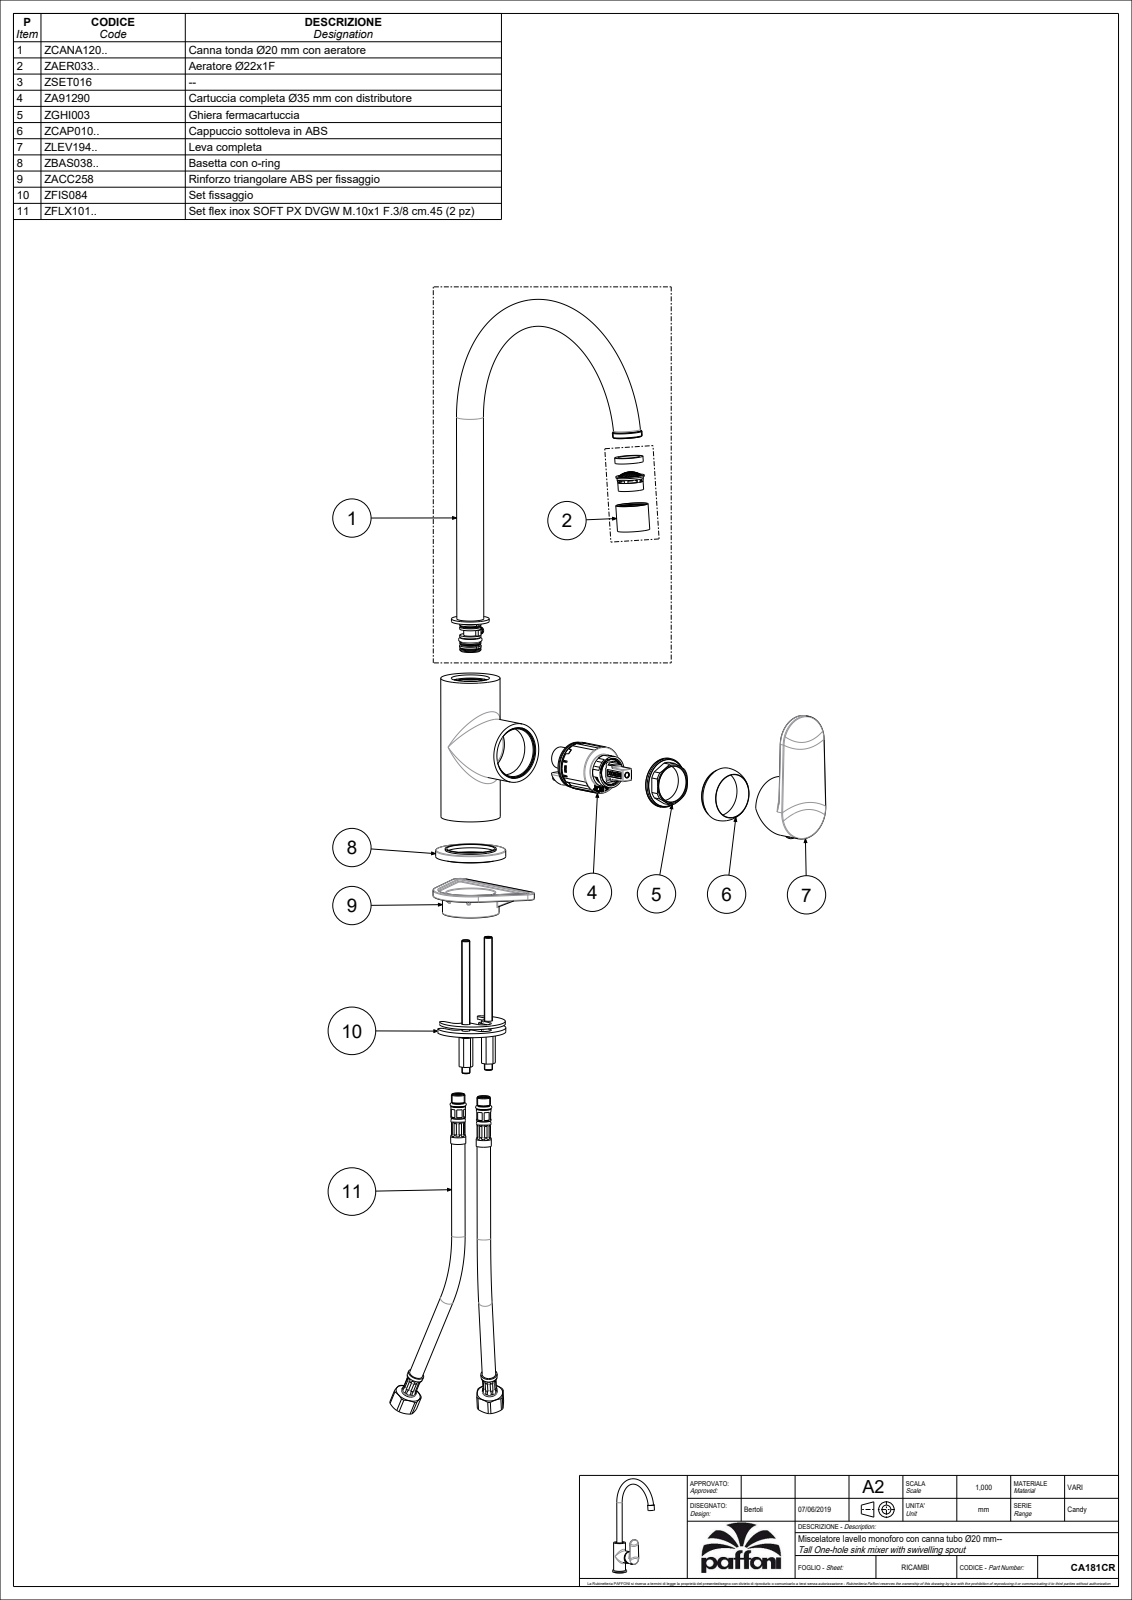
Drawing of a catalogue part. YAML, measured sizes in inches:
part_name: "CA181CR"
step_written_by: "CREO PARAMETRIC BY PTC INC, 2020044 (CONFIG_CONTROL_DESIGN)"
units: inches
bodies: {solids: 2, faces: 346, planar: 93, cylindrical: 139, other: 114}
overall_size: [14.265, 8.597, 4.37]
volume: 18.13
surface_area: 142.7
round_holes:
  - {diameter: 0.217, count: 3}
  - {diameter: 0.118, count: 2}
  - {diameter: 0.197, count: 2}
  - {diameter: 0.315, count: 2}
  - {diameter: 0.354, count: 2}
  - {diameter: 0.433, count: 2}
  - {diameter: 0.157, count: 1}
  - {diameter: 0.177, count: 1}
  - {diameter: 0.236, count: 1}
  - {diameter: 0.295, count: 1}
  - {diameter: 0.63, count: 1}
  - {diameter: 0.669, count: 1}
round_bosses_or_shafts:
  - {diameter: 1.732, count: 2}
  - {diameter: 0.299, count: 2}
  - {diameter: 2.047, count: 1}
  - {diameter: 1.693, count: 1}
  - {diameter: 1.488, count: 1}
  - {diameter: 1.102, count: 1}
  - {diameter: 0.945, count: 1}
  - {diameter: 0.787, count: 1}
partial_cylinders:
  - {radius: 0.118, count: 4}
  - {radius: 0.138, count: 1}
  - {radius: 0.787, count: 1}
  - {radius: 0.863, count: 1}
face_to_face_distances: [4.309, 4.311, 3.051, 1.339, 1.337, 2.972, 1.142, 0.197, 0.195, 4.114]
hole_center_spacings: [0.339, 0.378, 0.513, 0.53, 0.53, 0.596, 0.863, 0.89]
